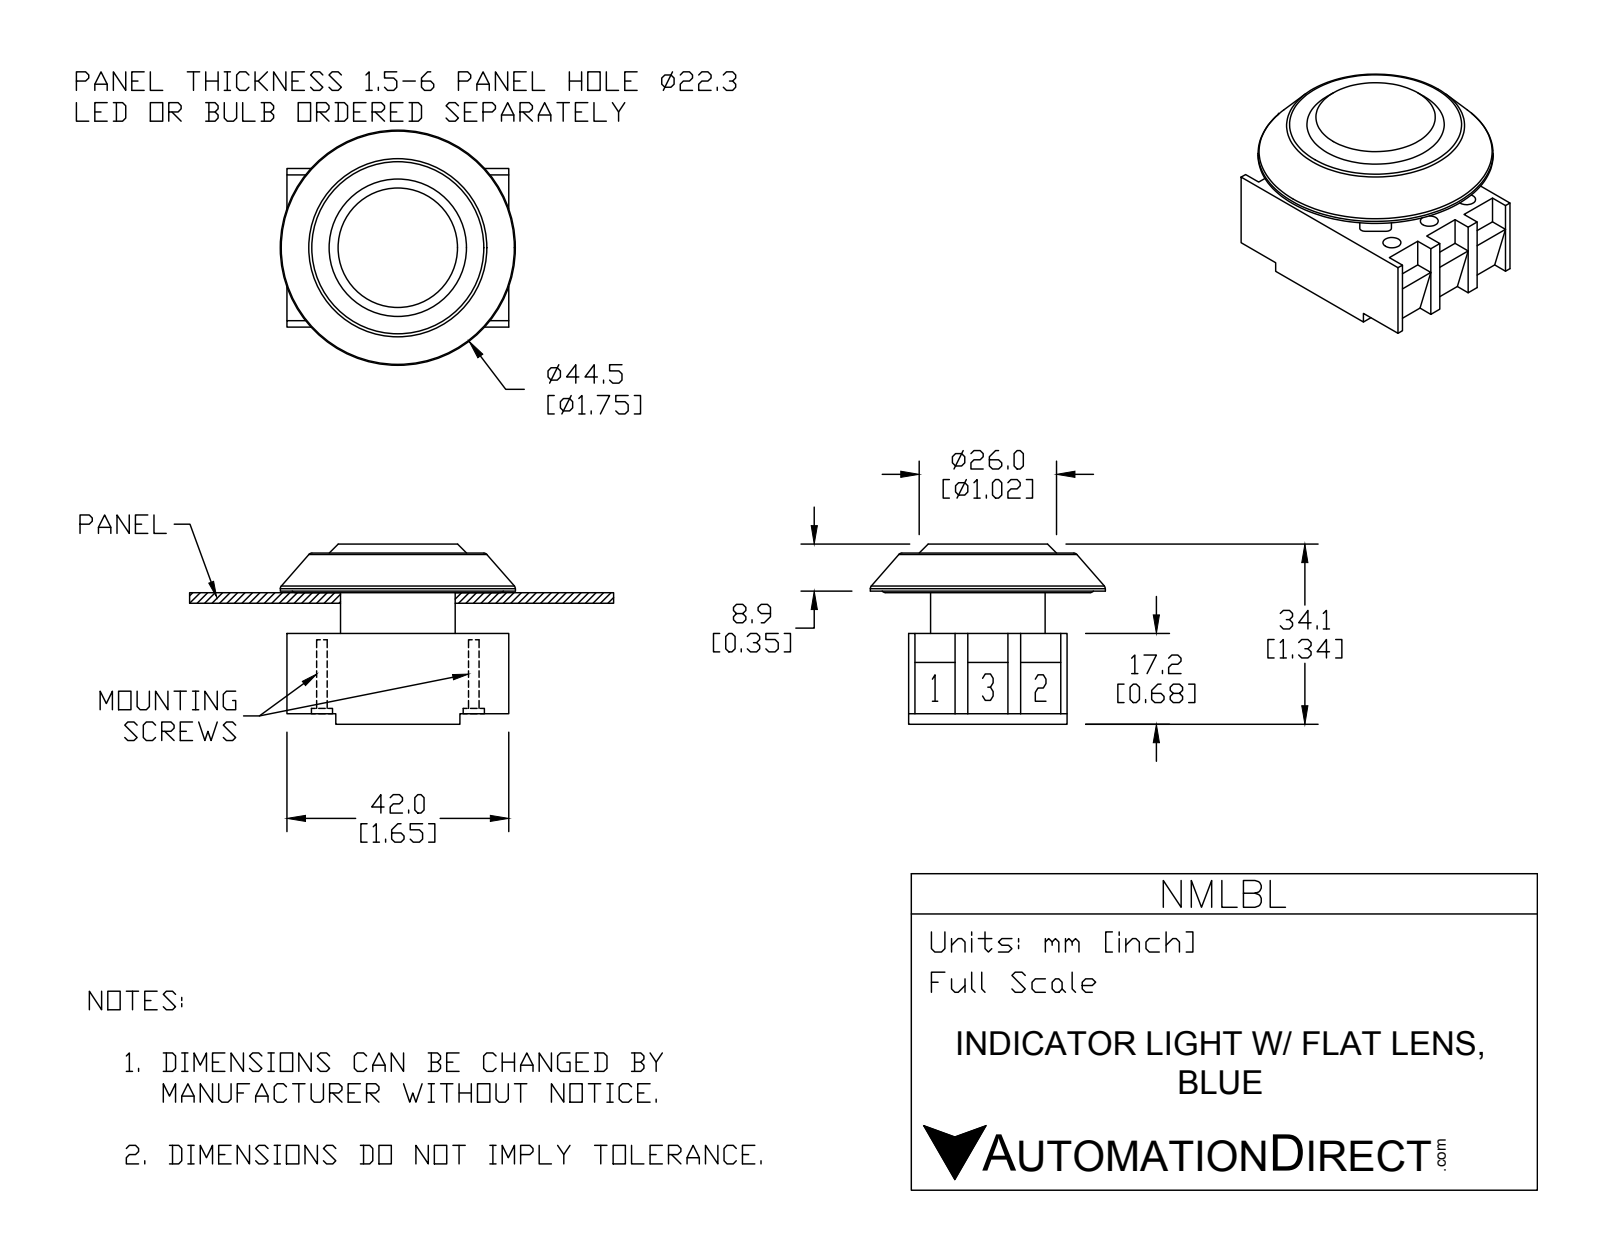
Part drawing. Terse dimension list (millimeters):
name: NMLBL
written by: SolidWorks 2015 (AUTOMOTIVE_DESIGN)
unit: mm
bodies: 6 solids, 209 faces (125 planar, 63 cylindrical, 21 other)
size: 44.5 × 44.5 × 34.1
volume: 23 947 mm³; area: 15 137 mm²
holes: 6× ⌀3.4, 6× ⌀5, 1× ⌀12.5
bosses: 2× ⌀4.6, 2× ⌀4, 1× ⌀44.5, 1× ⌀21.7
rounds: 8× R1, 5× R8.7, 1× R11
face distances: 30, 15.2, 8, 7.7, 9.2, 16.9, 8.9, 22.9, 10, 7.5
hole spacings: 10, 17.52, 30.45, 28.76, 14.38, 20, 35.03
